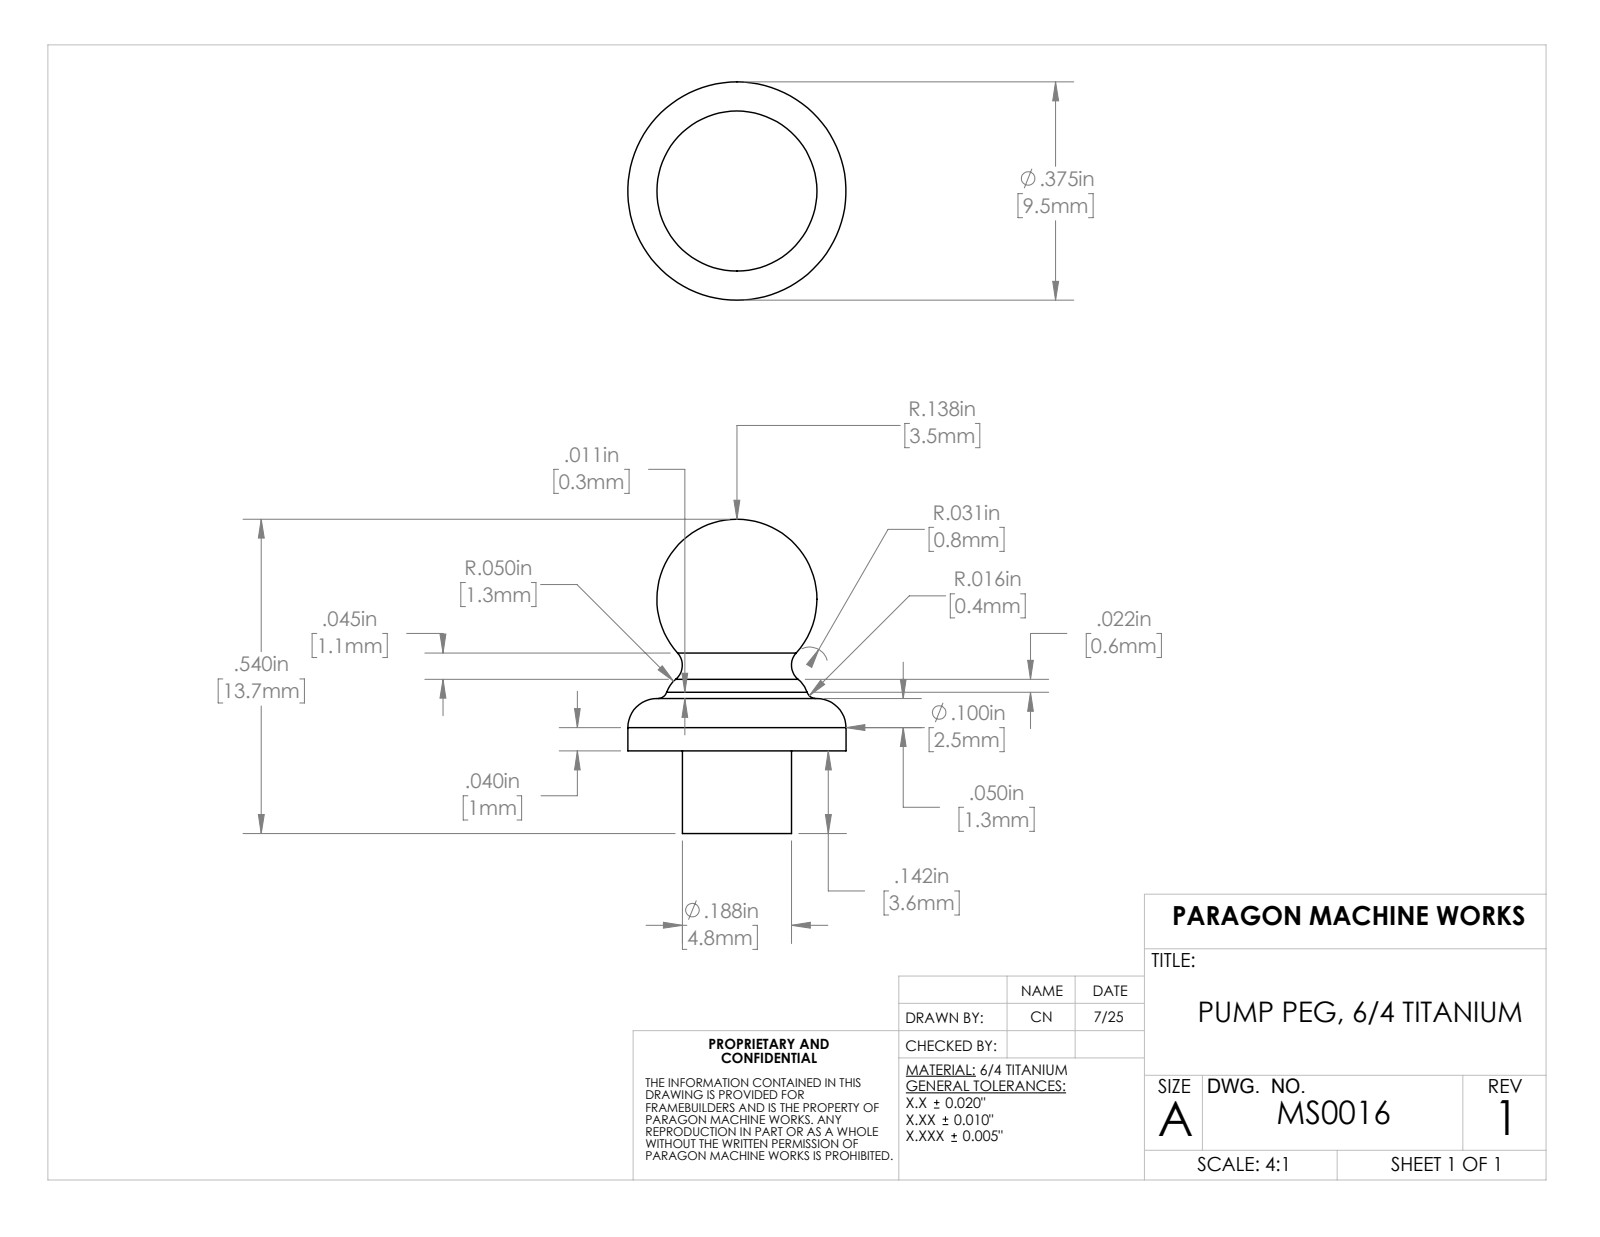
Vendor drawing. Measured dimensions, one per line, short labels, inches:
name: MS0016
written by: SolidWorks 2023 (AUTOMOTIVE_DESIGN)
unit: in
bodies: 1 solid, 18 faces (2 planar, 4 cylindrical, 12 other)
size: 0.54 × 0.375 × 0.375
volume: 0.026 in³; area: 0.591 in²
bosses: 1× ⌀0.375, 1× ⌀0.187
face distances: 0.142
